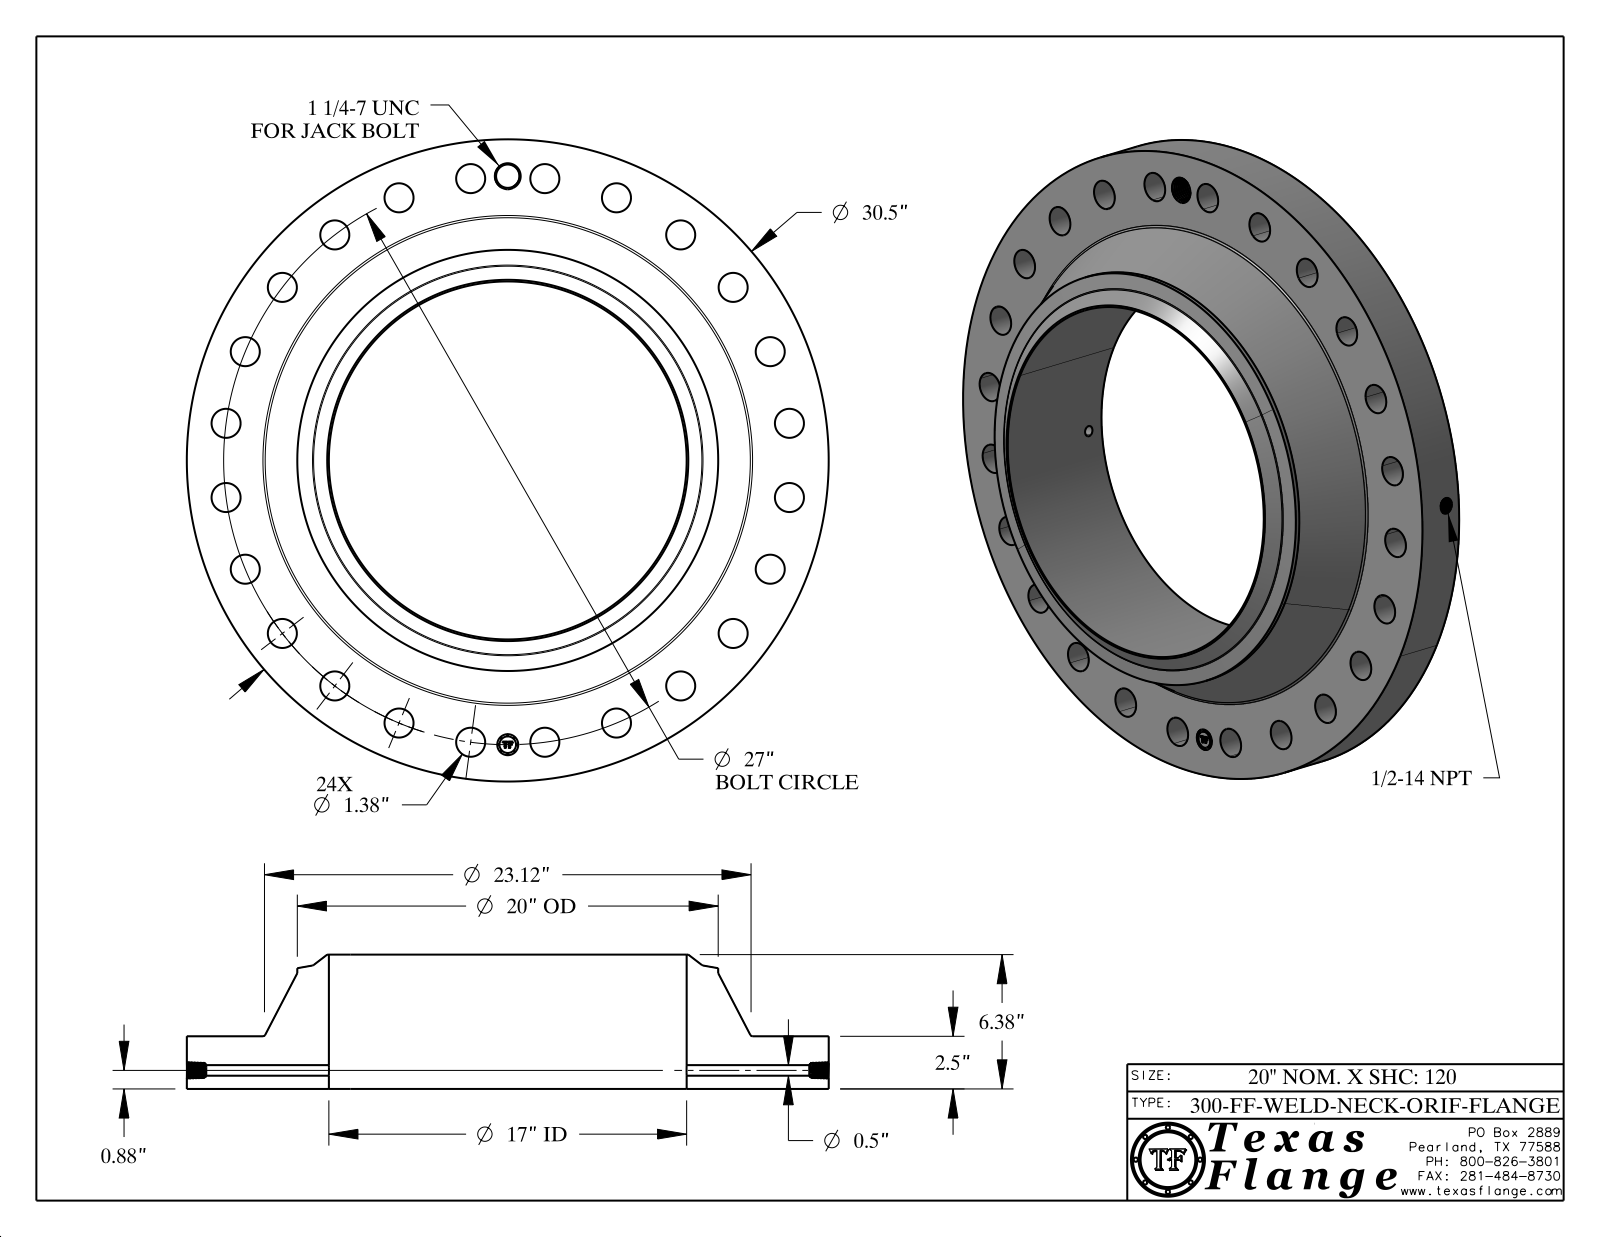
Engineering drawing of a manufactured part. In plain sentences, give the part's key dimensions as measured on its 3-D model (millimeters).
The part is named "300-FF-WELD-NECK". Its 3-D file was written by "CATIA V5 STEP AP214 (AUTOMOTIVE_DESIGN)". It is 1 solid with 819 faces: 368 planar, 129 cylindrical and 322 other. Overall it measures 774.7 by 774.7 by 162.1 millimeters. Its volume is 26 550 000 cubic millimeters and its surface area 1 264 000 square millimeters. Round holes: 24 of diameter 35.1, 1 of diameter 12.7, 1 of diameter 17.1, 1 of diameter 25.4, 1 of diameter 28.2, 1 of diameter 431.8. Round bosses or shafts: 8 of diameter 1.5, 1 of diameter 774.7, 1 of diameter 508, 1 of diameter 20. The main face-to-face distances are 63.5, 162.1, 98.6, 63.1, 0.4, 98.9, 7.6, 7.4, 1.4, 6.3. The hole center spacings are 342.9, 593.9, 633.6, 544.1, 89.5, 177.5, 484.9, 662.4.
